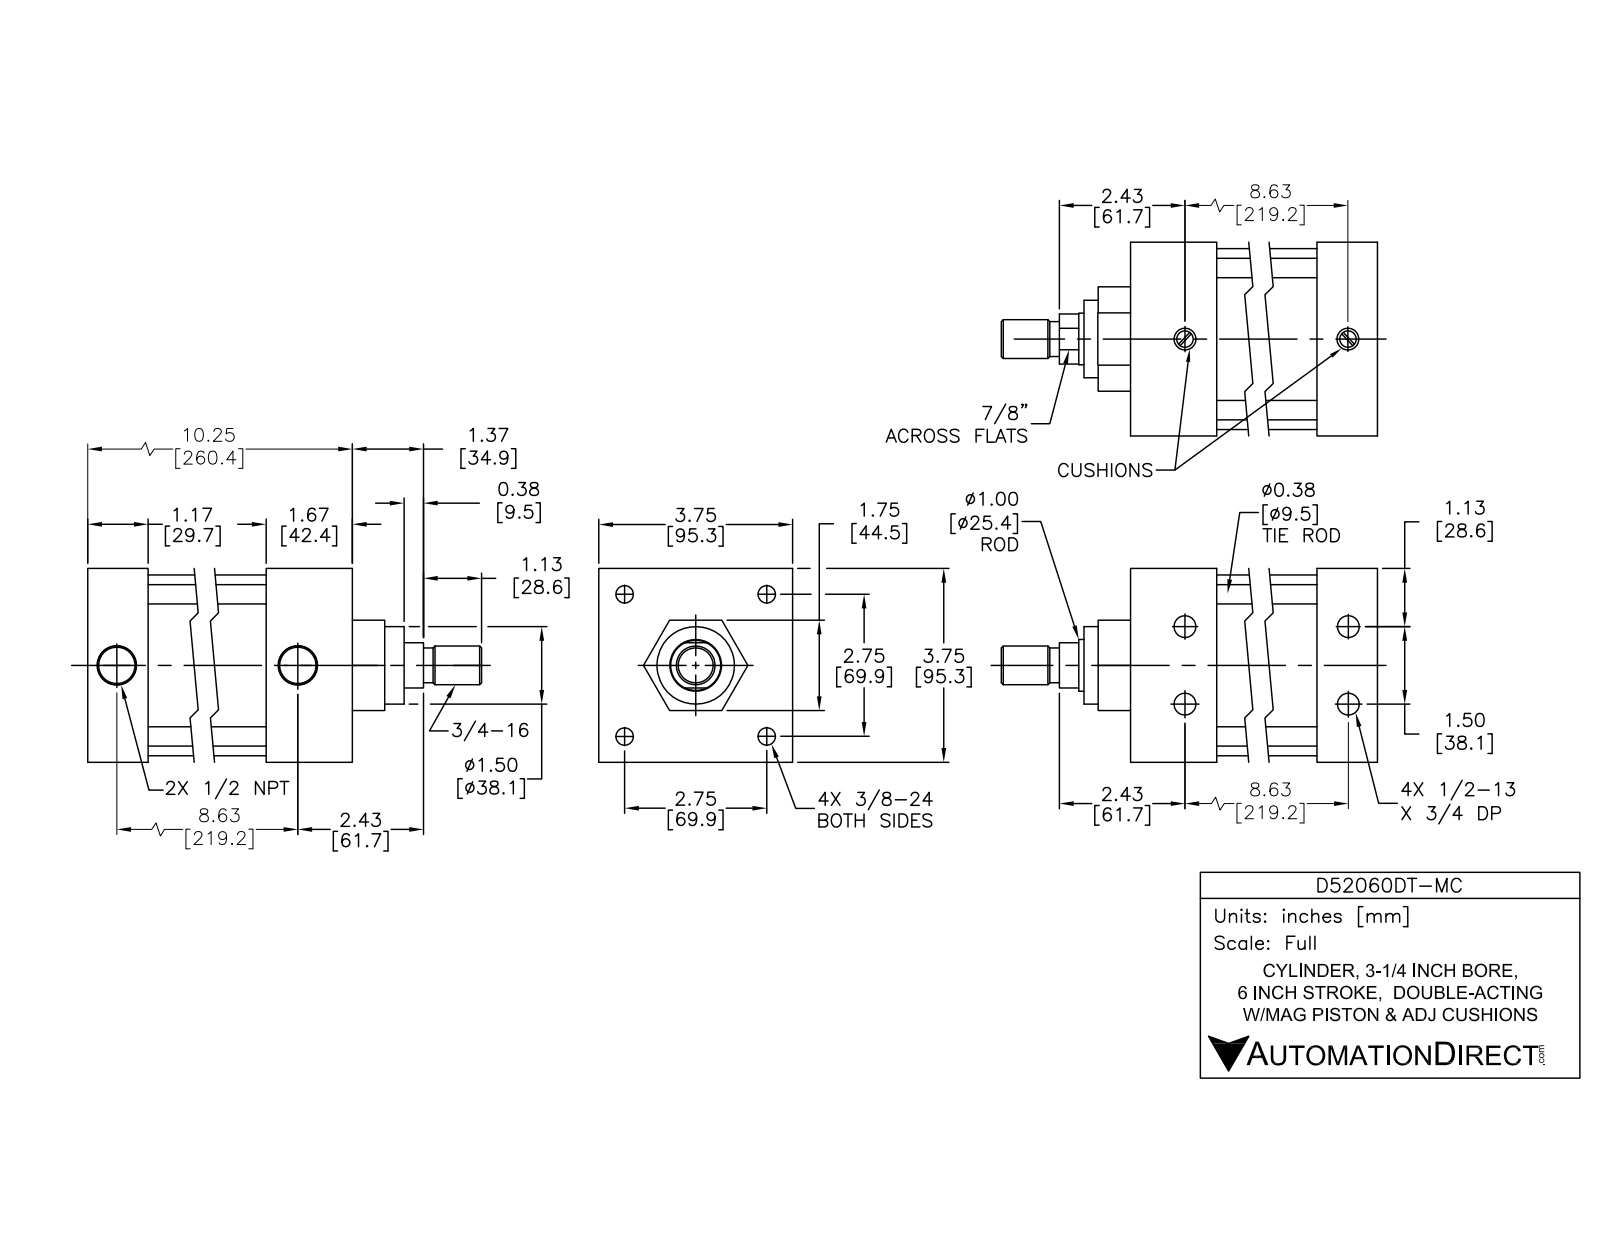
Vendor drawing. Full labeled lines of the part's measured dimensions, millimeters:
Part name (STEP PRODUCT): D52060DT-MC; D52060DT-M PISTON; D52060DT-M BODY
STEP written by: SolidWorks 2015 (AUTOMOTIVE_DESIGN)
Units: millimetres
Bodies: 12 solids, 303 faces (99 planar, 114 cylindrical, 90 other)
Overall size (bounding box): 323.7 × 95.3 × 95.3
Volume: 1 125 000 mm³ · Surface area: 263 700 mm²
Round holes (diameter × count): ⌀8.4 ×4, ⌀10.3 ×4, ⌀10.6 ×4, ⌀15.9 ×4, ⌀12.7 ×2, ⌀19.5 ×2, ⌀25.4 ×1, ⌀25.5 ×1, ⌀82.6 ×1
Round bosses / shafts (diameter × count): ⌀15.5 ×4, ⌀9.5 ×4, ⌀8.6 ×4, ⌀88.9 ×1, ⌀82.5 ×1, ⌀44.5 ×1, ⌀25.3 ×1, ⌀24.6 ×1
Partial cylindrical surfaces — rounded edges, fillets, slot ends (radius × count): R9.5 ×4
Main face-to-face distances: 95.3, 2, 186.1, 260.2, 44.5, 228.5, 31.7, 196.9, 31.6, 63.4
Hole centre spacings: 70.1, 49.5, 19.1, 19.3, 38.1, 99.1, 215.9, 216.8
